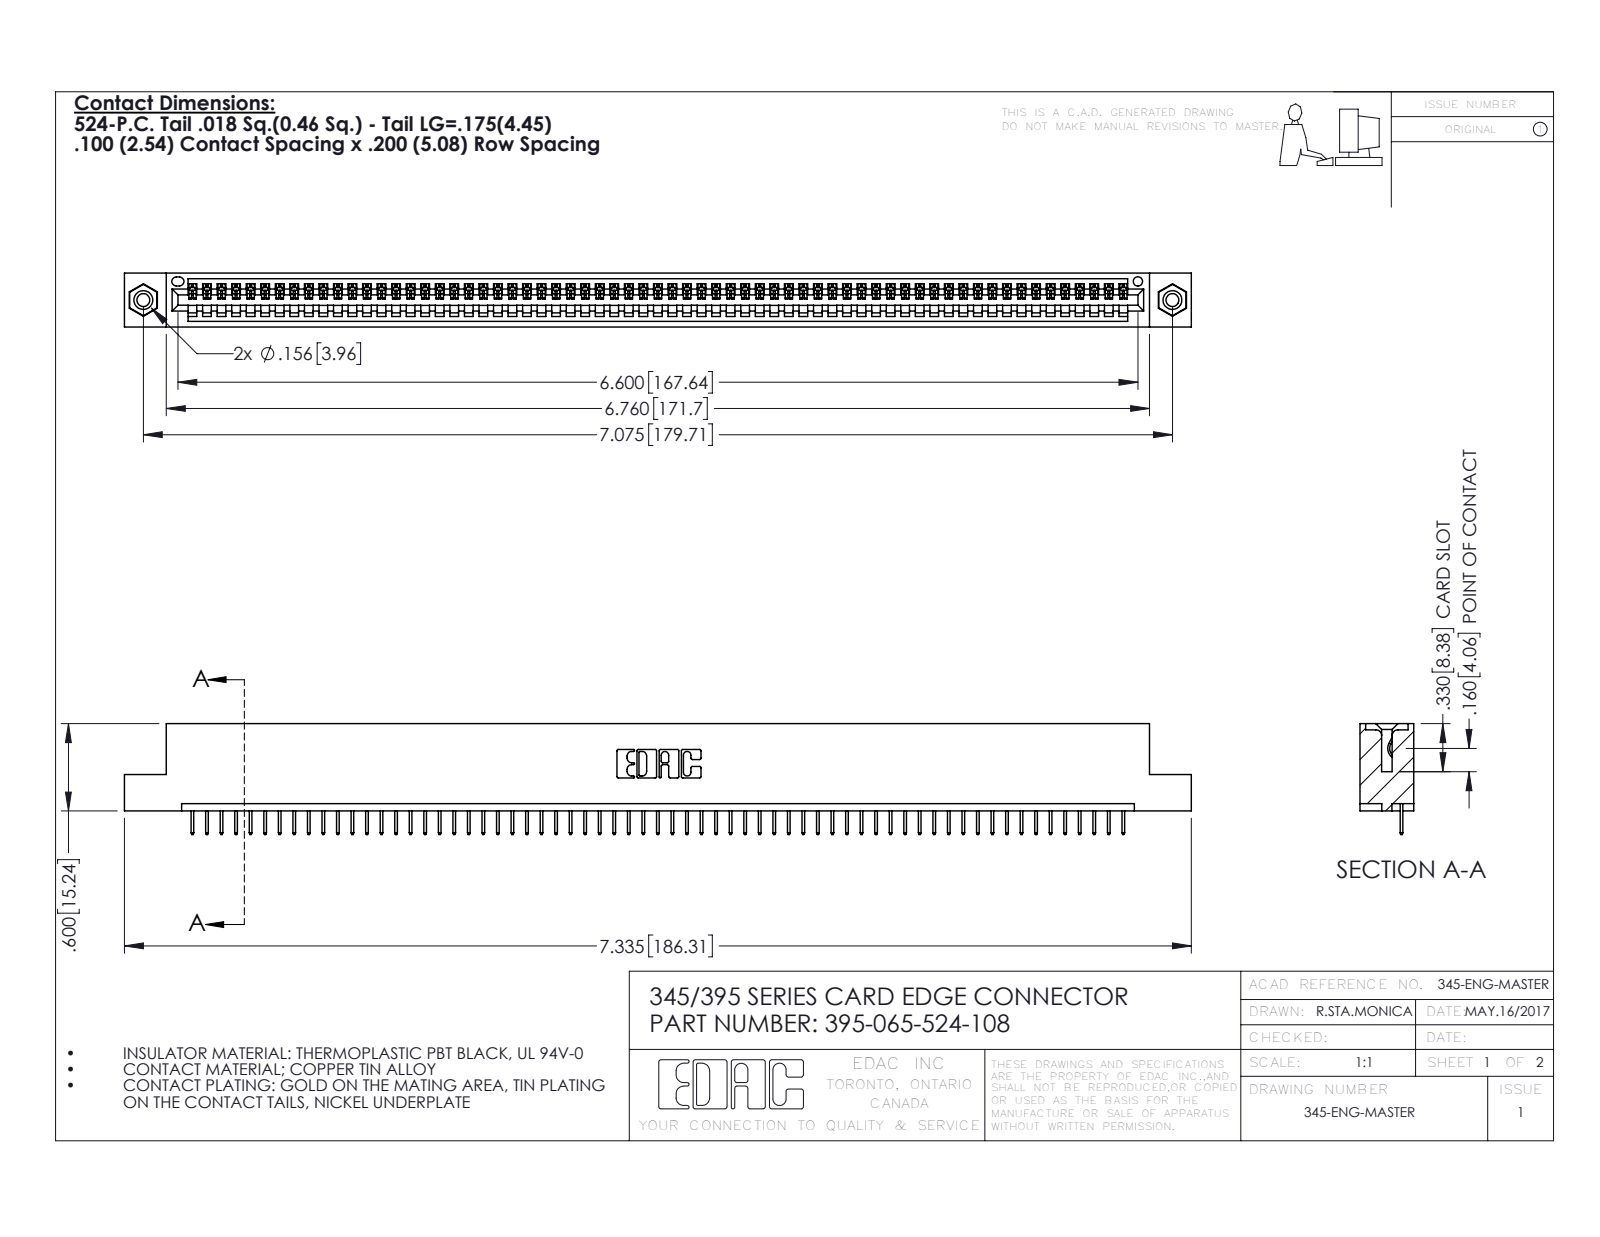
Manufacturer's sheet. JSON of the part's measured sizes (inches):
{"part_name": "395-065-524-108; 345-292-001_345-293-124; 345-250-001_345-250-003-102; 345 Part_Flush Mounting Lugs - 0.156 Dia-TI", "step_written_by": "SolidWorks 2016 (CONFIG_CONTROL_DESIGN)", "units": "inches", "bodies": {"solids": 68, "faces": 4216, "planar": 3102, "cylindrical": 1098, "other": 16}, "overall_size": [7.335, 0.762, 0.37], "volume_in3": 1.075, "surface_area_in2": 35.54, "round_holes": [[0.089, 2], [0.125, 2], [0.156, 2], [0.064, 1]], "round_bosses_or_shafts": [[0.155, 2]], "partial_cylinders_radius": [[0.006, 130], [0.01, 22], [0.007, 6], [0.031, 6], [0.026, 3], [0.031, 2], [0.04, 2], [0.014, 1]], "face_to_face_distances": [0.072, 0.298, 0.37, 0.2, 0.098, 0.272, 0.025, 0.225, 0.072, 0.149], "hole_center_spacings": [0.27, 6.839, 7.075]}
